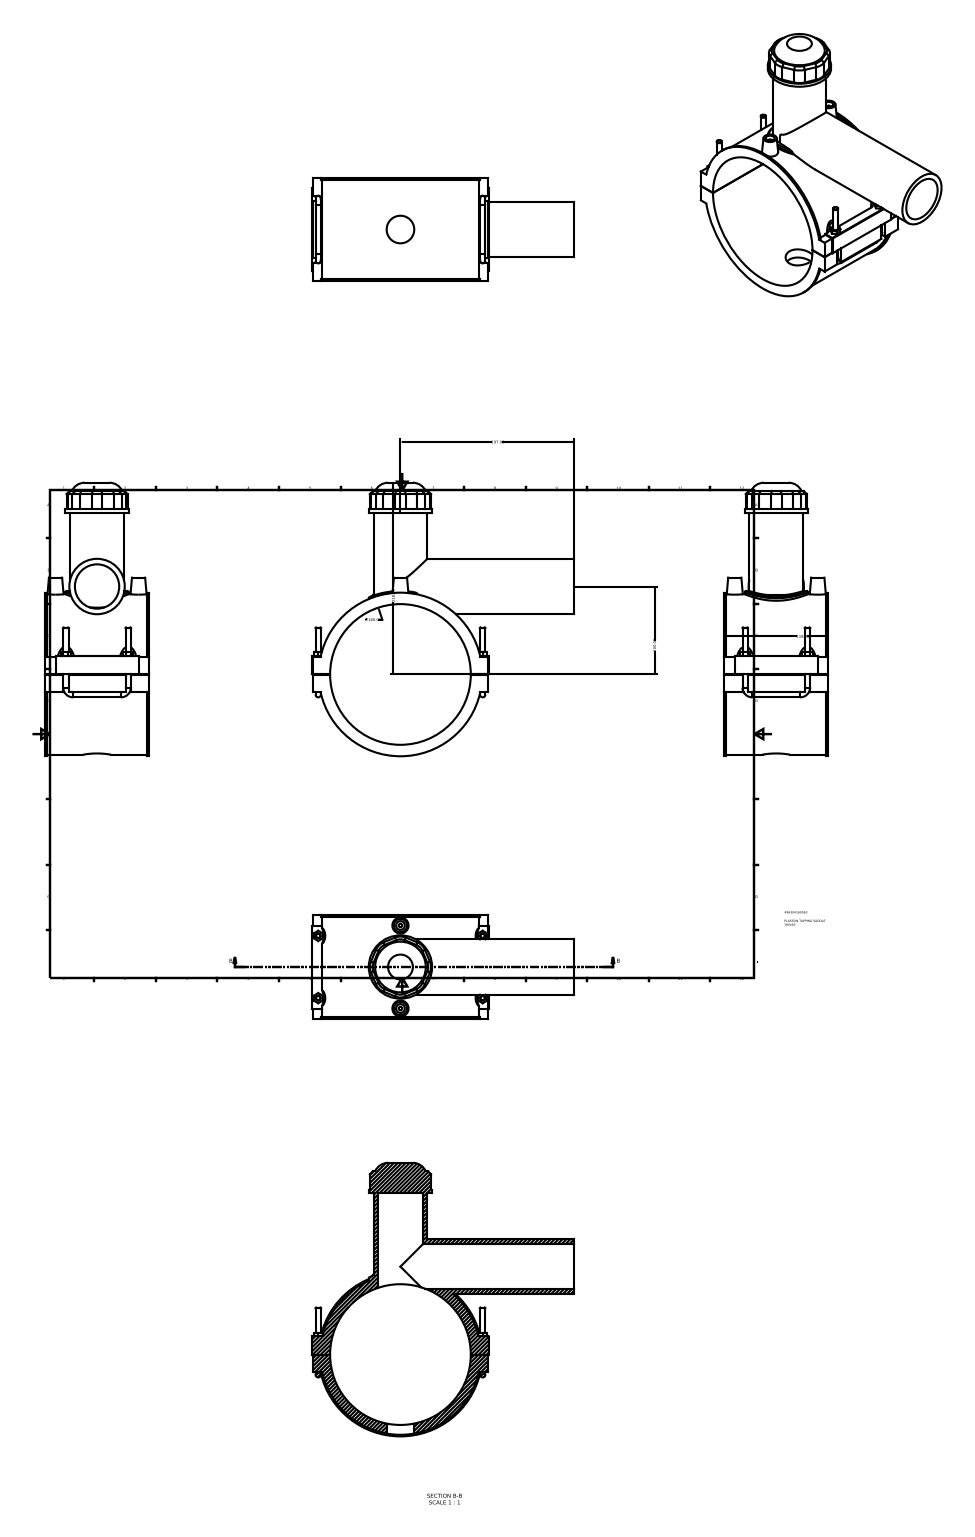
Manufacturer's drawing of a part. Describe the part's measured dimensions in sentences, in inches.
The part is named "496304160063". Its 3-D file was written by "Autodesk Inventor 2015 (AUTOMOTIVE_DESIGN)". It is 1 solid with 186 faces: 113 planar, 48 cylindrical and 25 other. Overall it measures 12.245 by 11.713 by 4.646 inches. Its volume is 70.79 cubic inches and its surface area 413.4 square inches. Round holes: 2 of diameter 0.394, 2 of diameter 1.984, 1 of diameter 1.235, 1 of diameter 6.299. Round bosses or shafts: 6 of diameter 0.236, 2 of diameter 0.157, 1 of diameter 7.325, 1 of diameter 7.181, 1 of diameter 2.835, 1 of diameter 2.48, 1 of diameter 2.409. Partial cylindrical surfaces (rounded edges, fillets, slot ends): 8 of radius 0.63, 4 of radius 0.118, 4 of radius 0.295, 1 of radius 0.02, 1 of radius 3.734. The main face-to-face distances are 4.646, 0.039, 7.874, 7.226, 7.222, 7.835, 0.785, 0.789, 8.012, 7.913. The hole center spacings are 1.858, 3.717.
